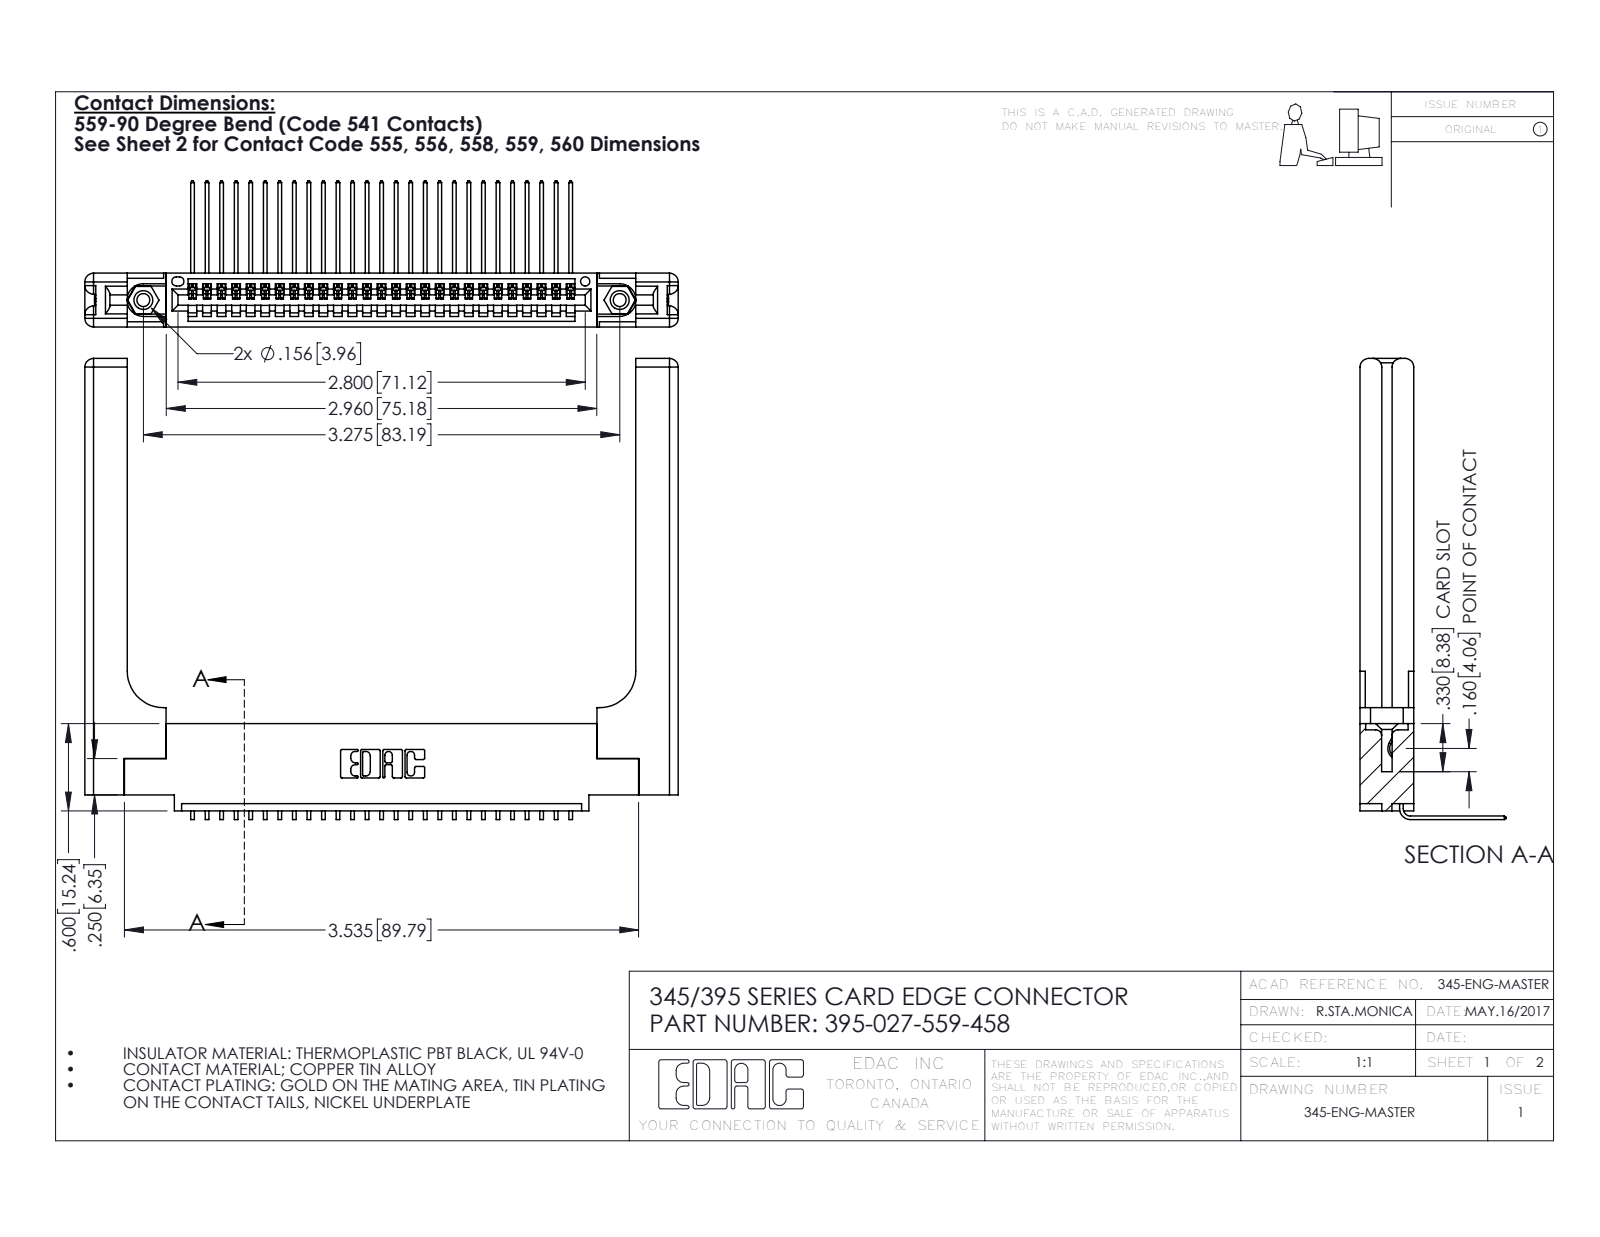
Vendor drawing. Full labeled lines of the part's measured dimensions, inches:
Part name (STEP PRODUCT): 345-292-001_558 559 Tail - 1; 345 Part_0.110 Offset - 0.156 Dia-TH; 345-220-058_345-220-058; 345-250-001_345-250-001-102 (+1 more)
STEP written by: SolidWorks 2016 (CONFIG_CONTROL_DESIGN)
Units: inches
Bodies: 32 solids, 2006 faces (1366 planar, 580 cylindrical, 60 other)
Overall size (bounding box): 4.079 × 3.169 × 1.005
Volume: 1.113 in³ · Surface area: 28.9 in²
Round holes (diameter × count): ⌀0.089 ×2, ⌀0.125 ×2, ⌀0.156 ×2, ⌀0.064 ×1
Round bosses / shafts (diameter × count): ⌀0.155 ×2
Partial cylindrical surfaces — rounded edges, fillets, slot ends (radius × count): R0.006 ×54, R0.01 ×22, R0.06 ×16, R0.007 ×6, R0.031 ×6, R0.026 ×3, R0.03 ×2, R0.031 ×2
Main face-to-face distances: 0.37, 0.072, 0.298, 0.148, 0.15, 0.077, 0.098, 0.272, 0.025, 0.2
Hole centre spacings: 0.27, 3.04, 3.275
